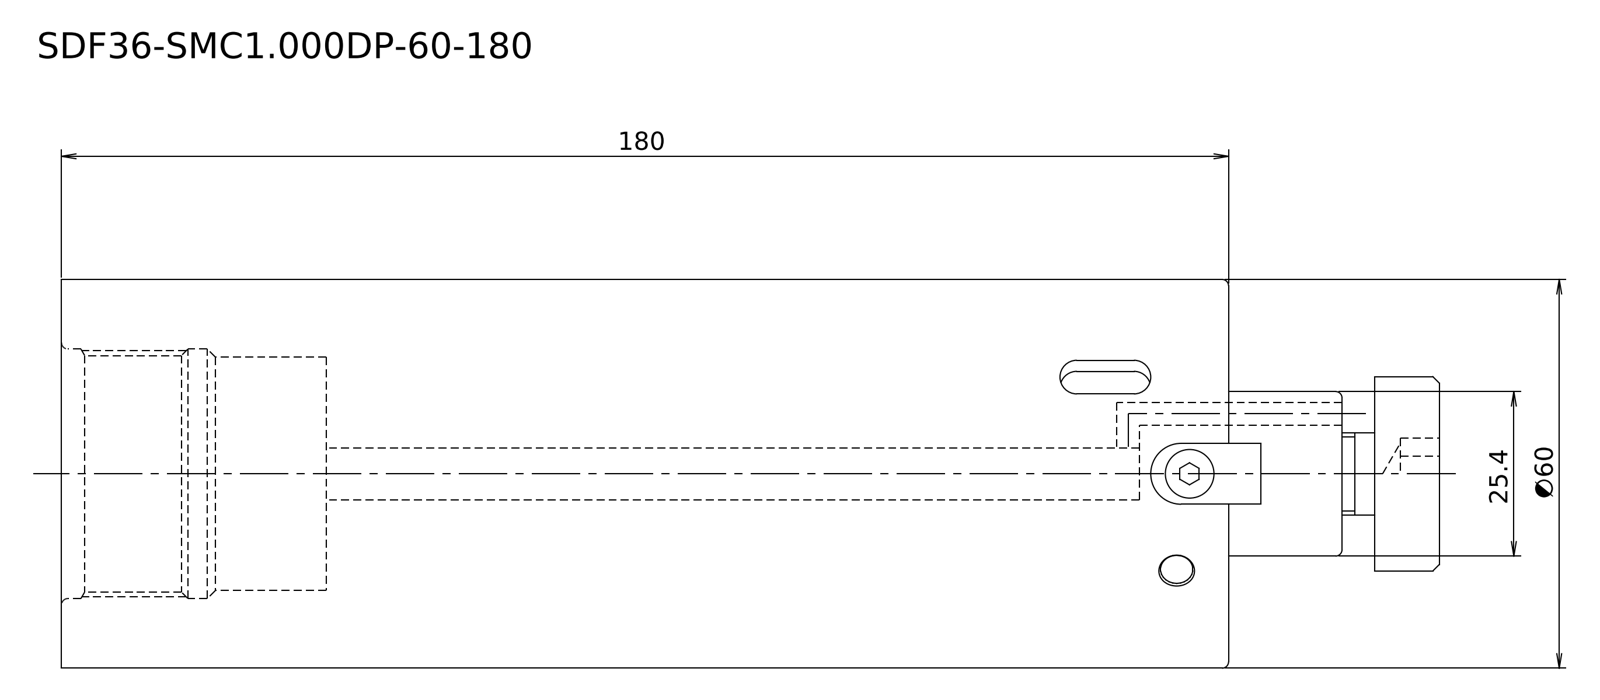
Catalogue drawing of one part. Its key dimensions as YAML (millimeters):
step_written_by: "Kubotek KeyCreator 2011 V10.0.2 (22737) (automotive_design)"
units: millimeters
bodies: {solids: 1, faces: 5, planar: 3, cylindrical: 2, other: 0}
overall_size: [197.5, 60, 60]
volume: 517805
surface_area: 40981
round_bosses_or_shafts:
  - {diameter: 60, count: 1}
  - {diameter: 25.4, count: 1}
face_to_face_distances: [180, 17.5, 197.5]
